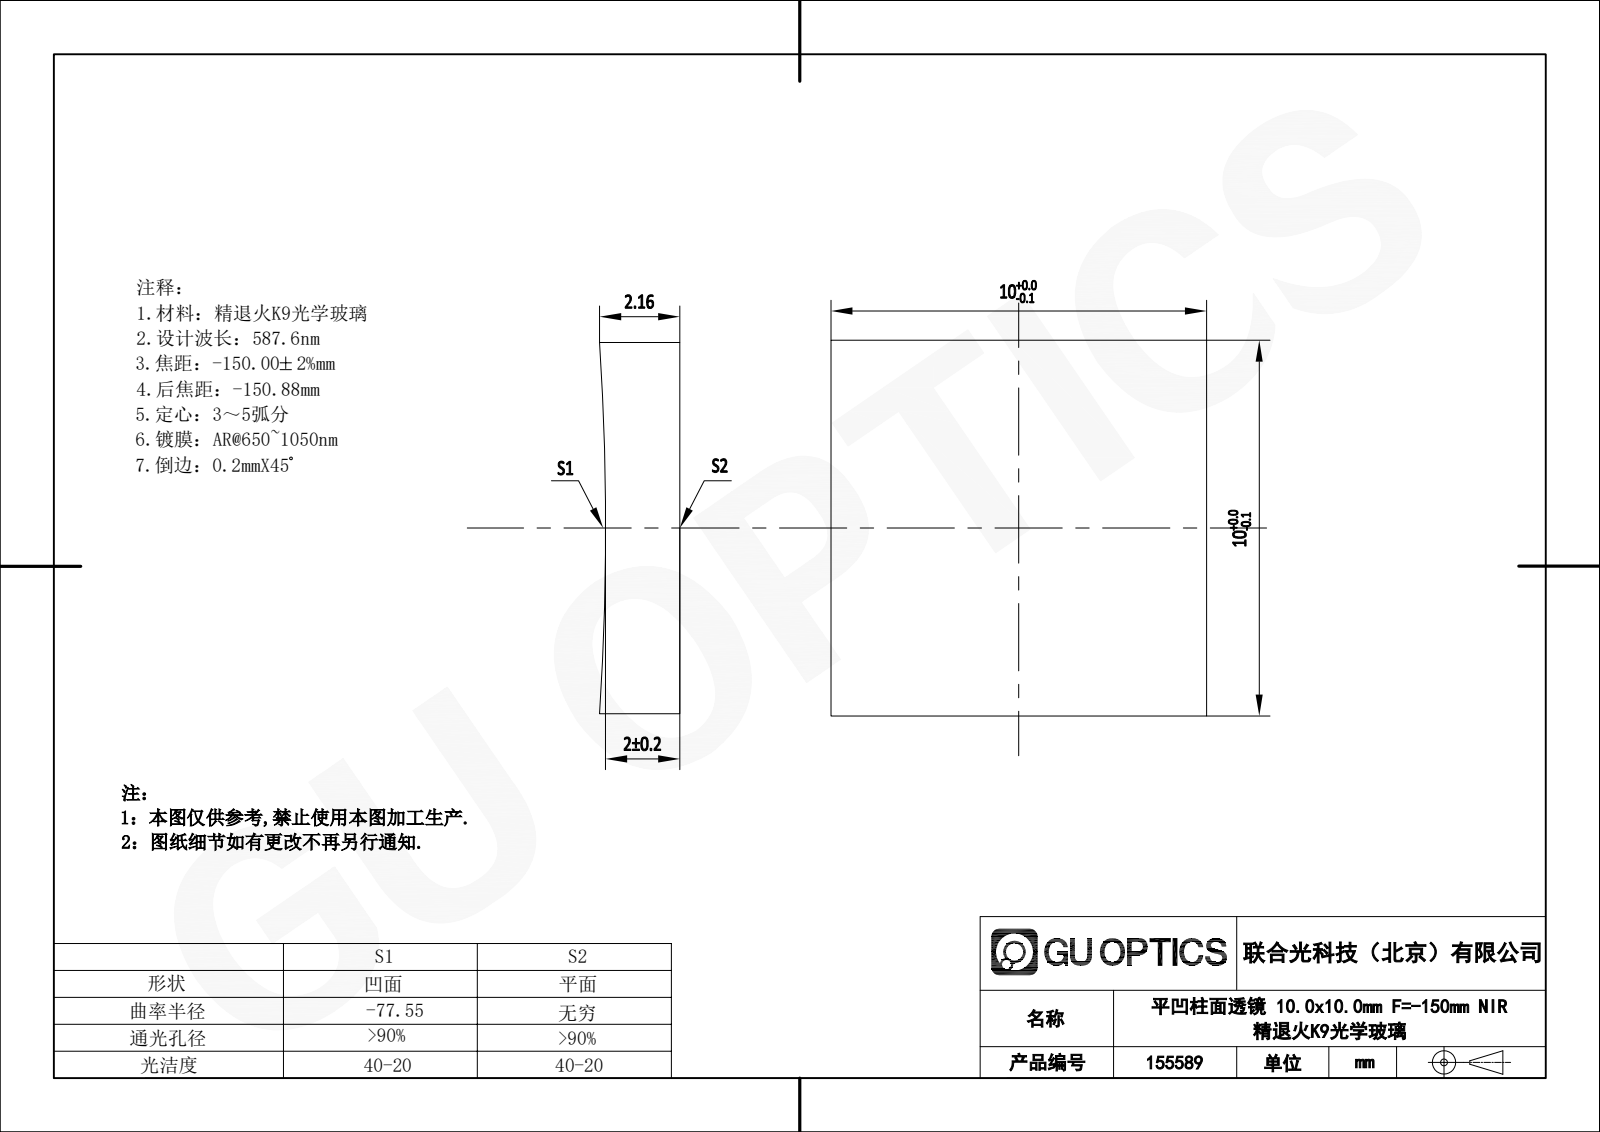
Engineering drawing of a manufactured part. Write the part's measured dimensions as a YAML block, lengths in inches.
part_name: "155569"
step_written_by: "SolidWorks 2020 (CONFIG_CONTROL_DESIGN)"
units: inches
bodies: {solids: 1, faces: 6, planar: 5, cylindrical: 1, other: 0}
overall_size: [0.394, 0.394, 0.085]
volume: 0.013
surface_area: 0.44
partial_cylinders:
  - {radius: 3.053, count: 1}
face_to_face_distances: [0.394]
